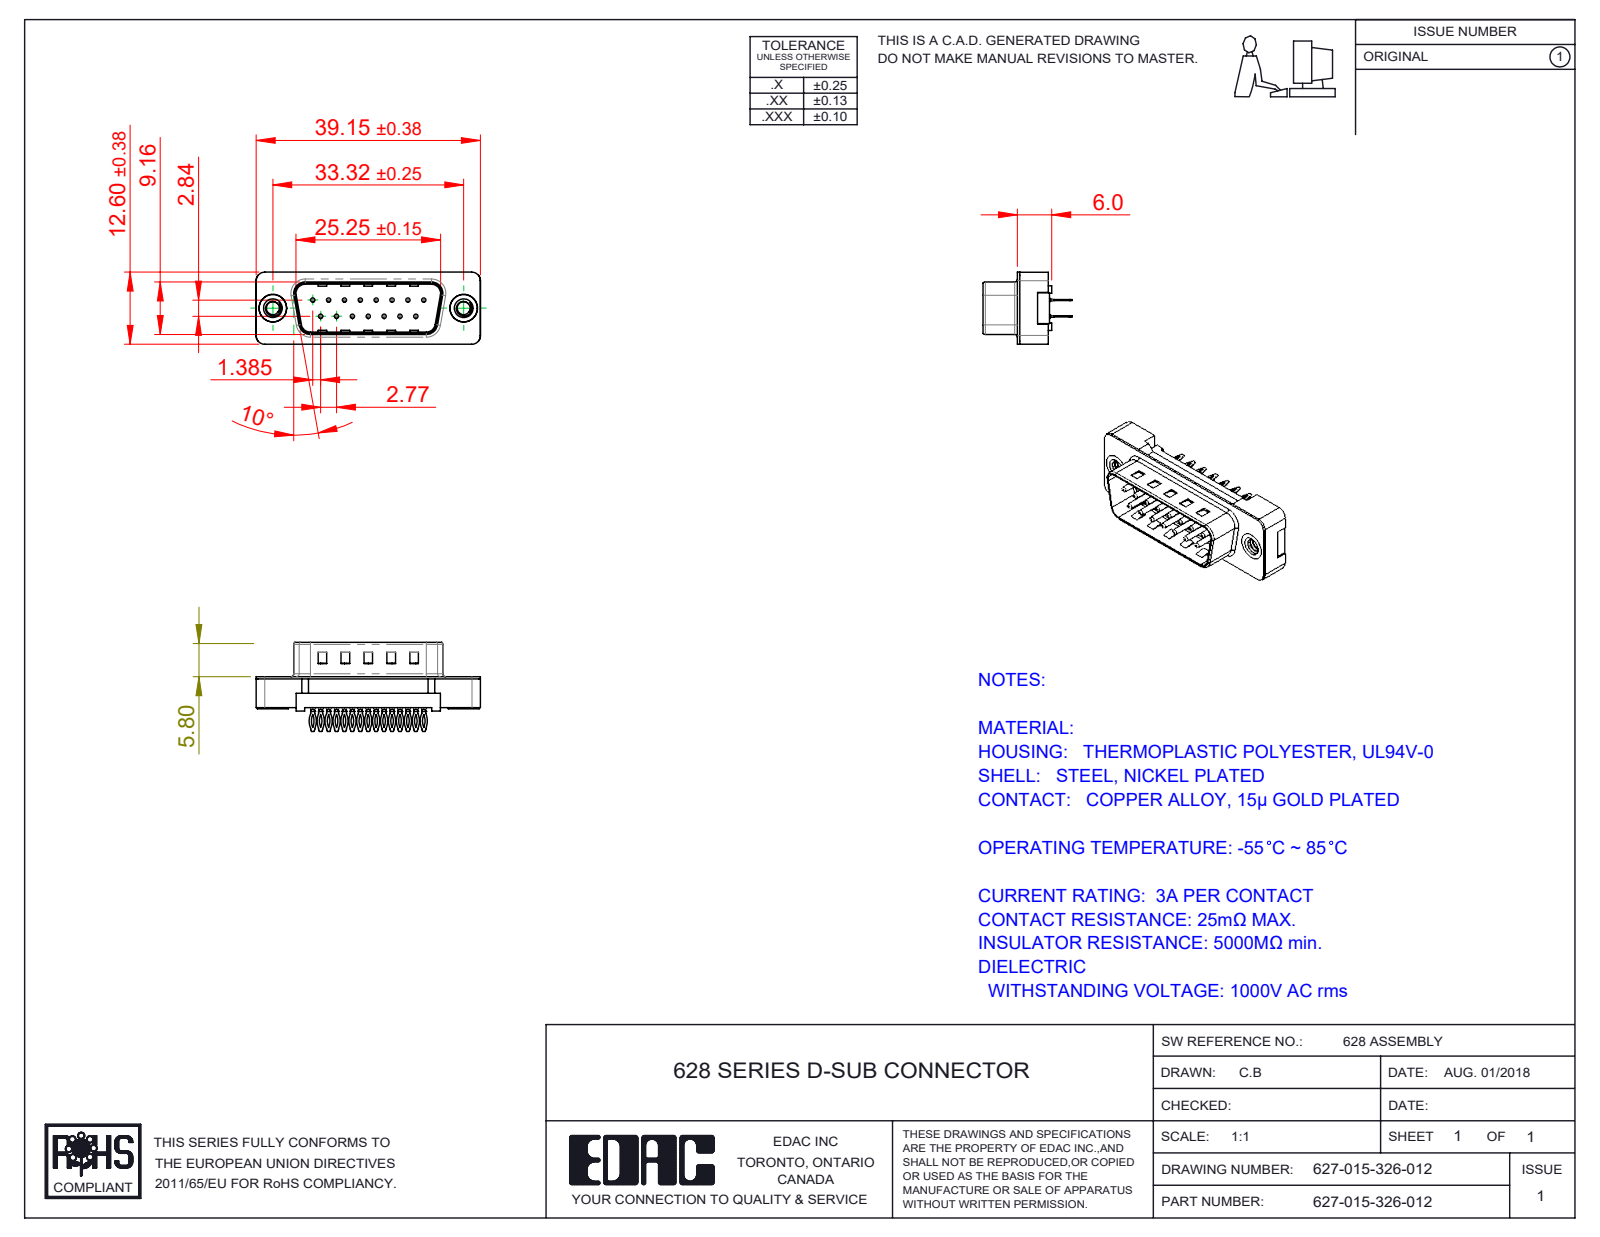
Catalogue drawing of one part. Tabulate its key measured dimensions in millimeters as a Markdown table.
| quantity | value |
| --- | --- |
| part name | 627 PB 4-40 Threaded Rivet; 627 Plastic Body Housing_15 Contacts; 627 PB Contact Row 2_26; 627 PB Contact Row 1_26 (+2 more) |
| STEP written by | SolidWorks 2020 (CONFIG_CONTROL_DESIGN) |
| units | millimeters |
| bodies | 19 solids, 1356 faces (816 planar, 400 cylindrical, 140 other) |
| overall size | 39.19 × 15.55 × 12.6 |
| volume | 1 982 mm³ |
| surface area | 4 271 mm² |
| round holes (diameter × count) | 0.35 × 15, 0.85 × 15, 2.26 × 2, 4 × 2, 4.8 × 2, 5 × 2 |
| round bosses / shafts (diameter × count) | 0.75 × 15, 4.9 × 2 |
| partial cylindrical surfaces (radius × count) | 0.25 × 30, 2.92 × 30, 3.33 × 30, 0.12 × 15, 0.5 × 8, 1.5 × 8, 0.9 × 4, 1.6 × 4 |
| main face-to-face distances | 0.4, 2.5, 5.4, 8.76, 5, 2.9, 8.48, 0.68, 8.08, 2.38 |
| hole center spacings | 3.16, 2.77, 5.54, 8.31, 5.03, 7.48, 11.08, 5.04 |
